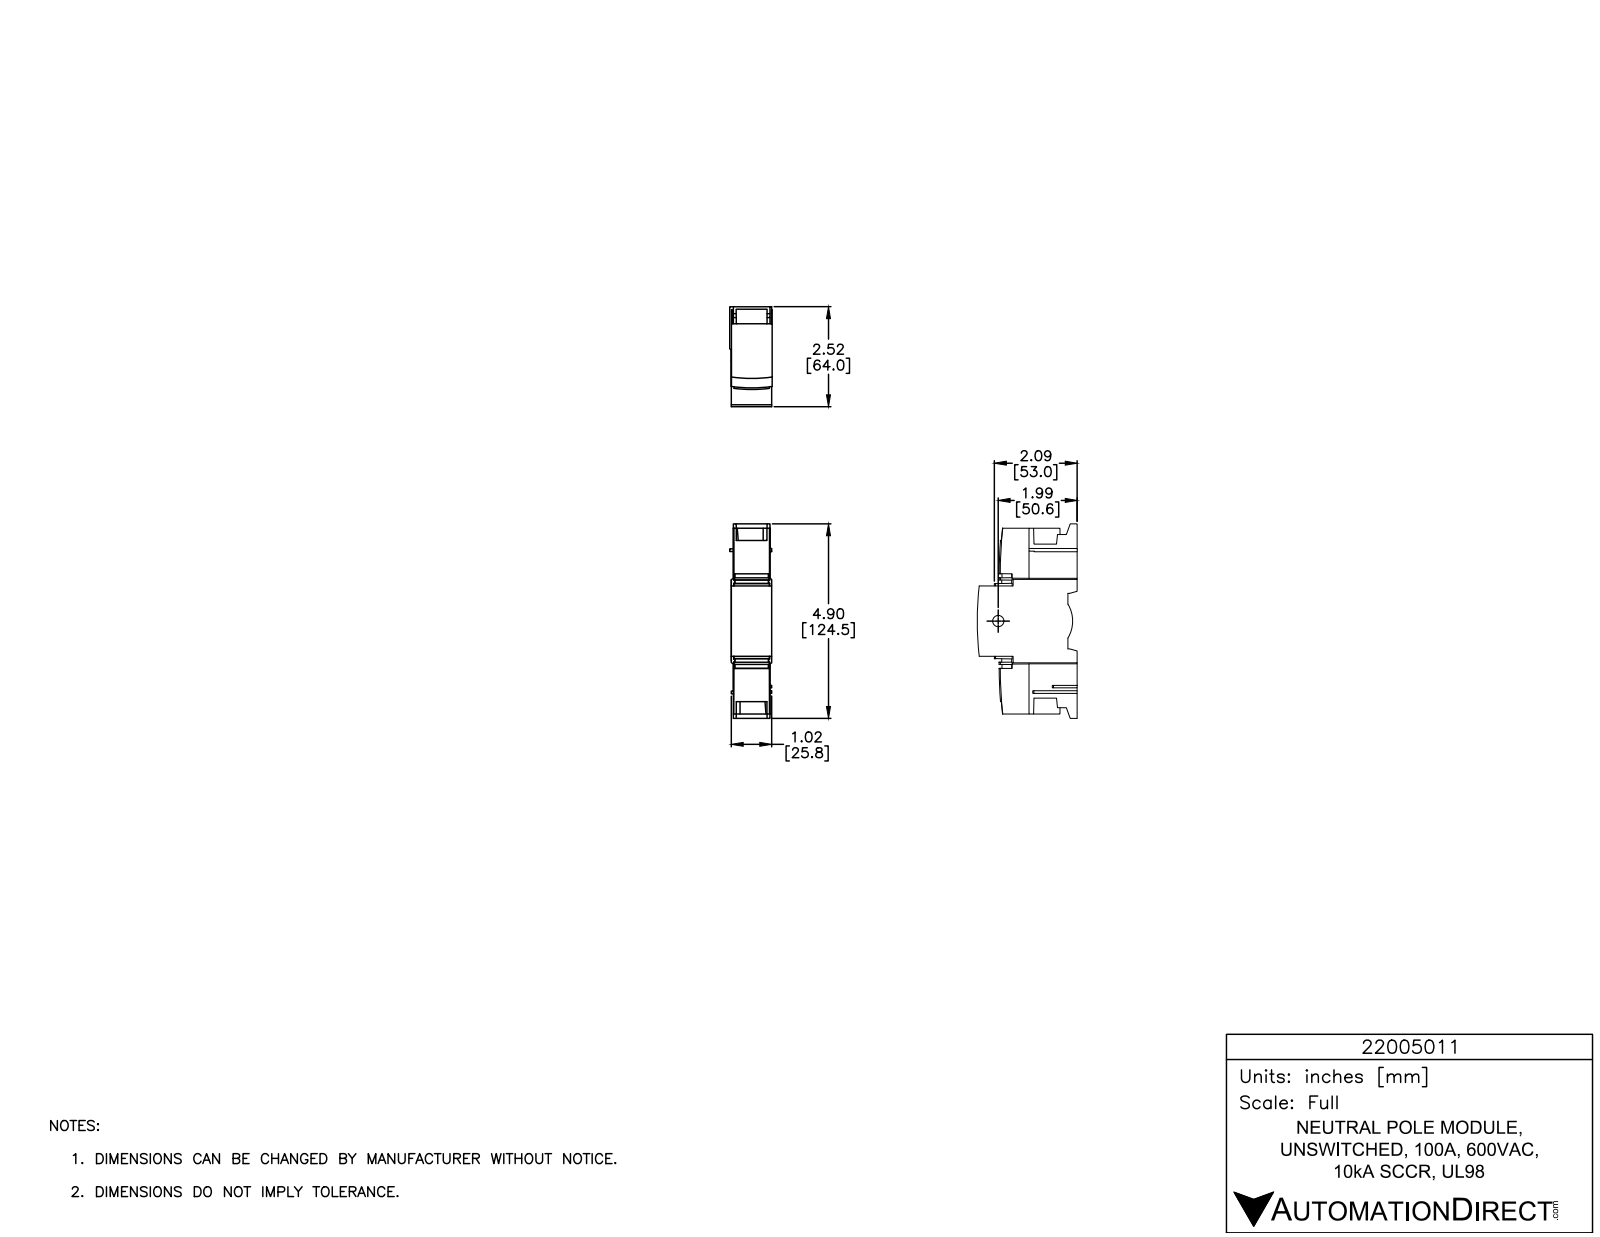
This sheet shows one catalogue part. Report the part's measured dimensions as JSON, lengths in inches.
{"part_name": "22005011", "step_written_by": "SolidWorks 2015 (AUTOMOTIVE_DESIGN)", "units": "inches", "bodies": {"solids": 1, "faces": 166, "planar": 151, "cylindrical": 11, "other": 4}, "overall_size": [4.902, 2.519, 1.055], "volume_in3": 7.941, "surface_area_in2": 43.37, "round_holes": [[0.283, 1]], "partial_cylinders_radius": [[0.827, 1], [3.543, 1], [3.646, 1], [7.874, 1]], "face_to_face_distances": [1.016, 0.051, 0.965, 0.972, 0.921, 0.043, 0.553, 0.169, 0.752, 1.189]}
